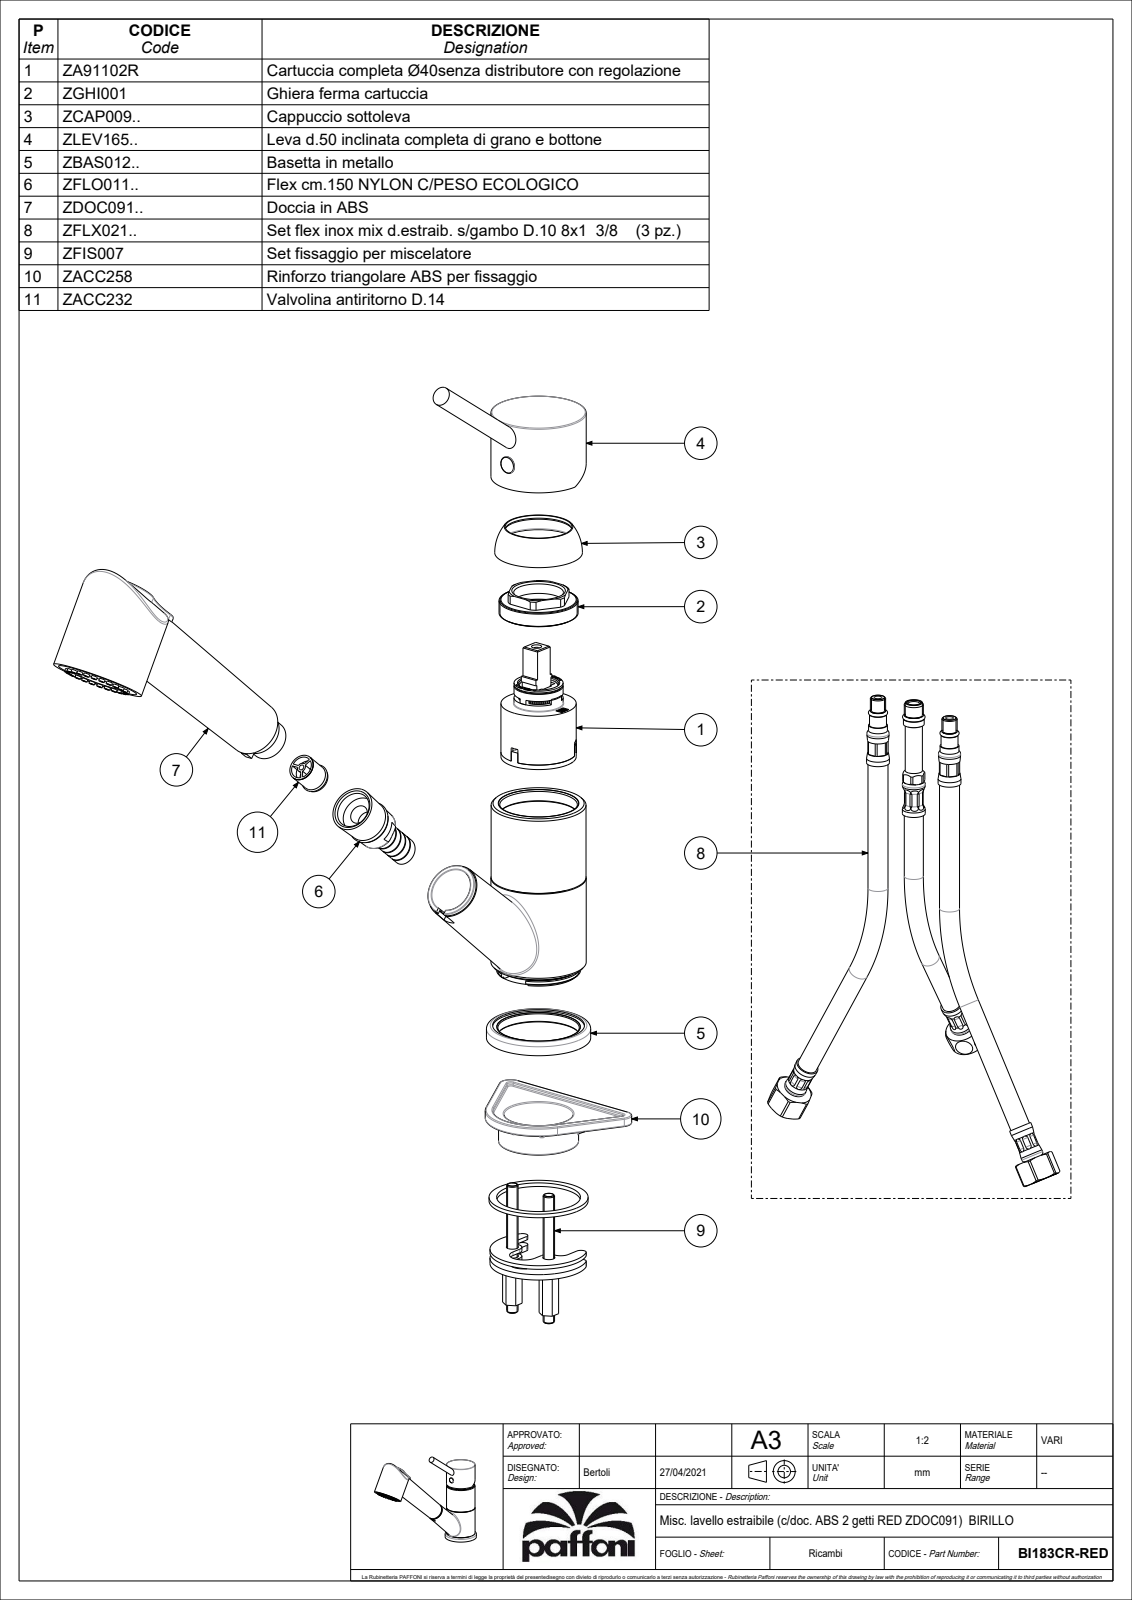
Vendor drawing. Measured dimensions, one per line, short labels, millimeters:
name: BI183CR-RED
written by: CREO PARAMETRIC BY PTC INC, 2020044 (CONFIG_CONTROL_DESIGN)
unit: mm
bodies: 2 solids, 1267 faces (582 planar, 410 cylindrical, 275 other)
size: 247.32 × 189.13 × 54.7
volume: 359 630 mm³; area: 128 190 mm²
holes: 24× ⌀1.5, 5× ⌀7, 2× ⌀3.3, 2× ⌀5.5, 2× ⌀8, 2× ⌀8.6, 2× ⌀9.4, 2× ⌀11, 2× ⌀11.7, 1× ⌀3, 1× ⌀4, 1× ⌀4.2
bosses: 24× ⌀3, 1× ⌀54.7, 1× ⌀50, 1× ⌀49.8, 1× ⌀49, 1× ⌀48, 1× ⌀44.8, 1× ⌀44.7
rounds: 24× R0.2, 22× R0.5, 8× R1, 2× R12.5, 2× R50, 1× R2.5, 1× R3, 1× R3.75
face distances: 64.9, 45.5, 3.1, 7, 0.5, 10.8, 21.4, 43.5, 18.3, 46.6
hole spacings: 16.5, 12.63, 20.09, 26.18, 28.58, 30.49, 32.72, 8.54
